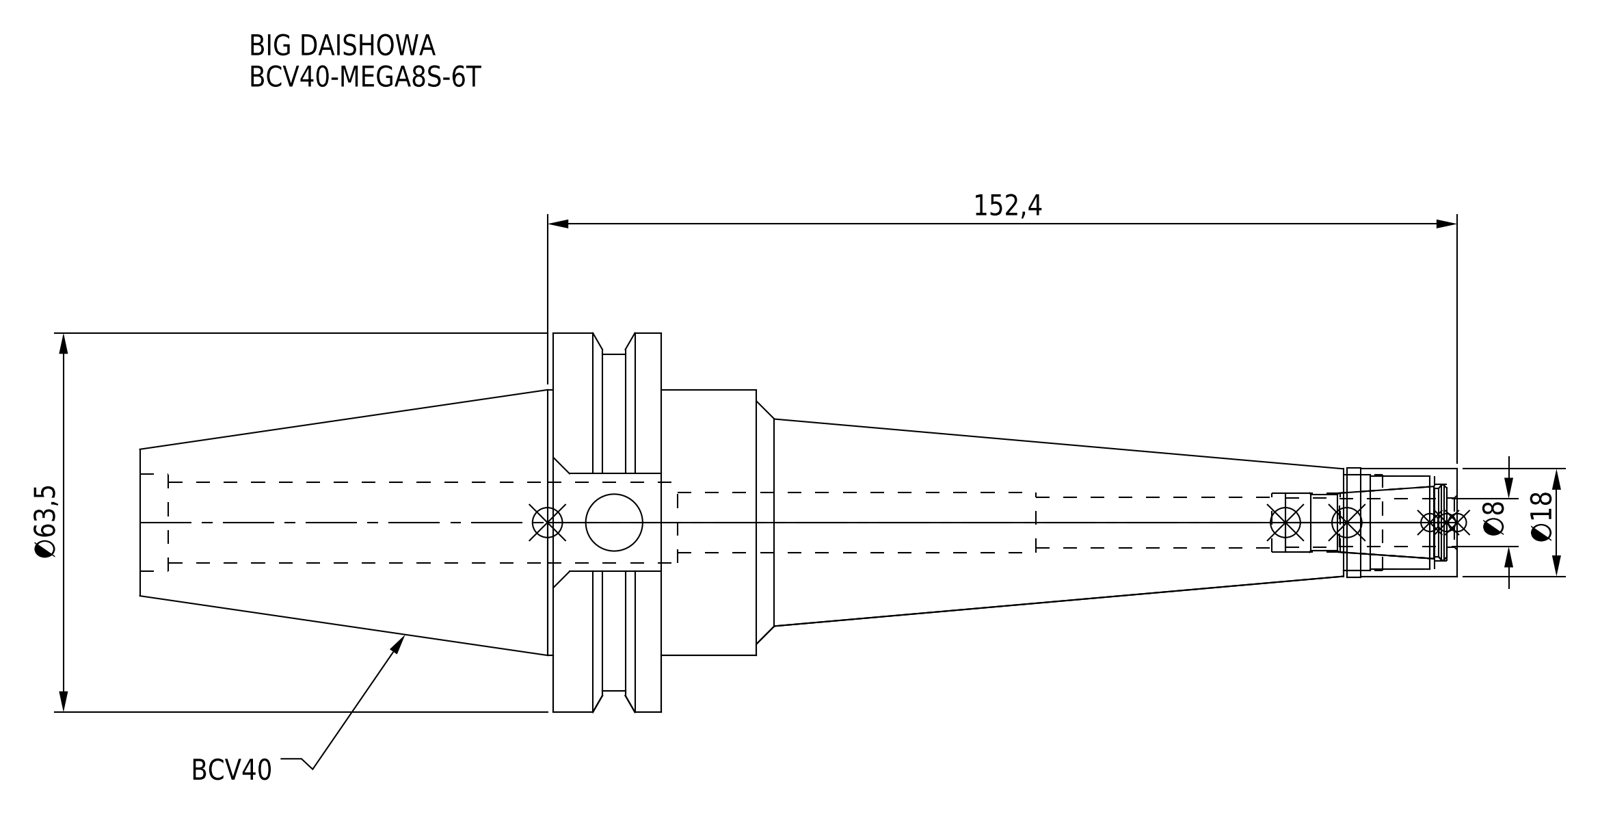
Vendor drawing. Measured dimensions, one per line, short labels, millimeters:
name: BCV40-MEGA8S-6T; BCV40-MEGA8S-6T_1.stp; BCV40-MEGA8S-6T-080.stp; MGN8S_1.stp (+3 more)
written by: SolidWorks 2019 (CONFIG_CONTROL_DESIGN)
unit: mm
bodies: 2 solids, 86 faces (32 planar, 40 cylindrical, 14 other)
size: 220.65 × 63.5 × 61.35
volume: 180 284 mm³; area: 37 154 mm²
holes: 1× ⌀8.2, 1× ⌀8.4, 1× ⌀9.53, 1× ⌀9.9, 1× ⌀10, 1× ⌀12.9, 1× ⌀13.6, 1× ⌀15.6, 1× ⌀16.1, 1× ⌀16.32
bosses: 1× ⌀63.5, 1× ⌀56.36, 1× ⌀44.45, 1× ⌀18.3, 1× ⌀18
face distances: 18.05, 87.3, 69.25, 15.95, 34, 103.25, 47.55, 117.4, 133.35, 151.4
